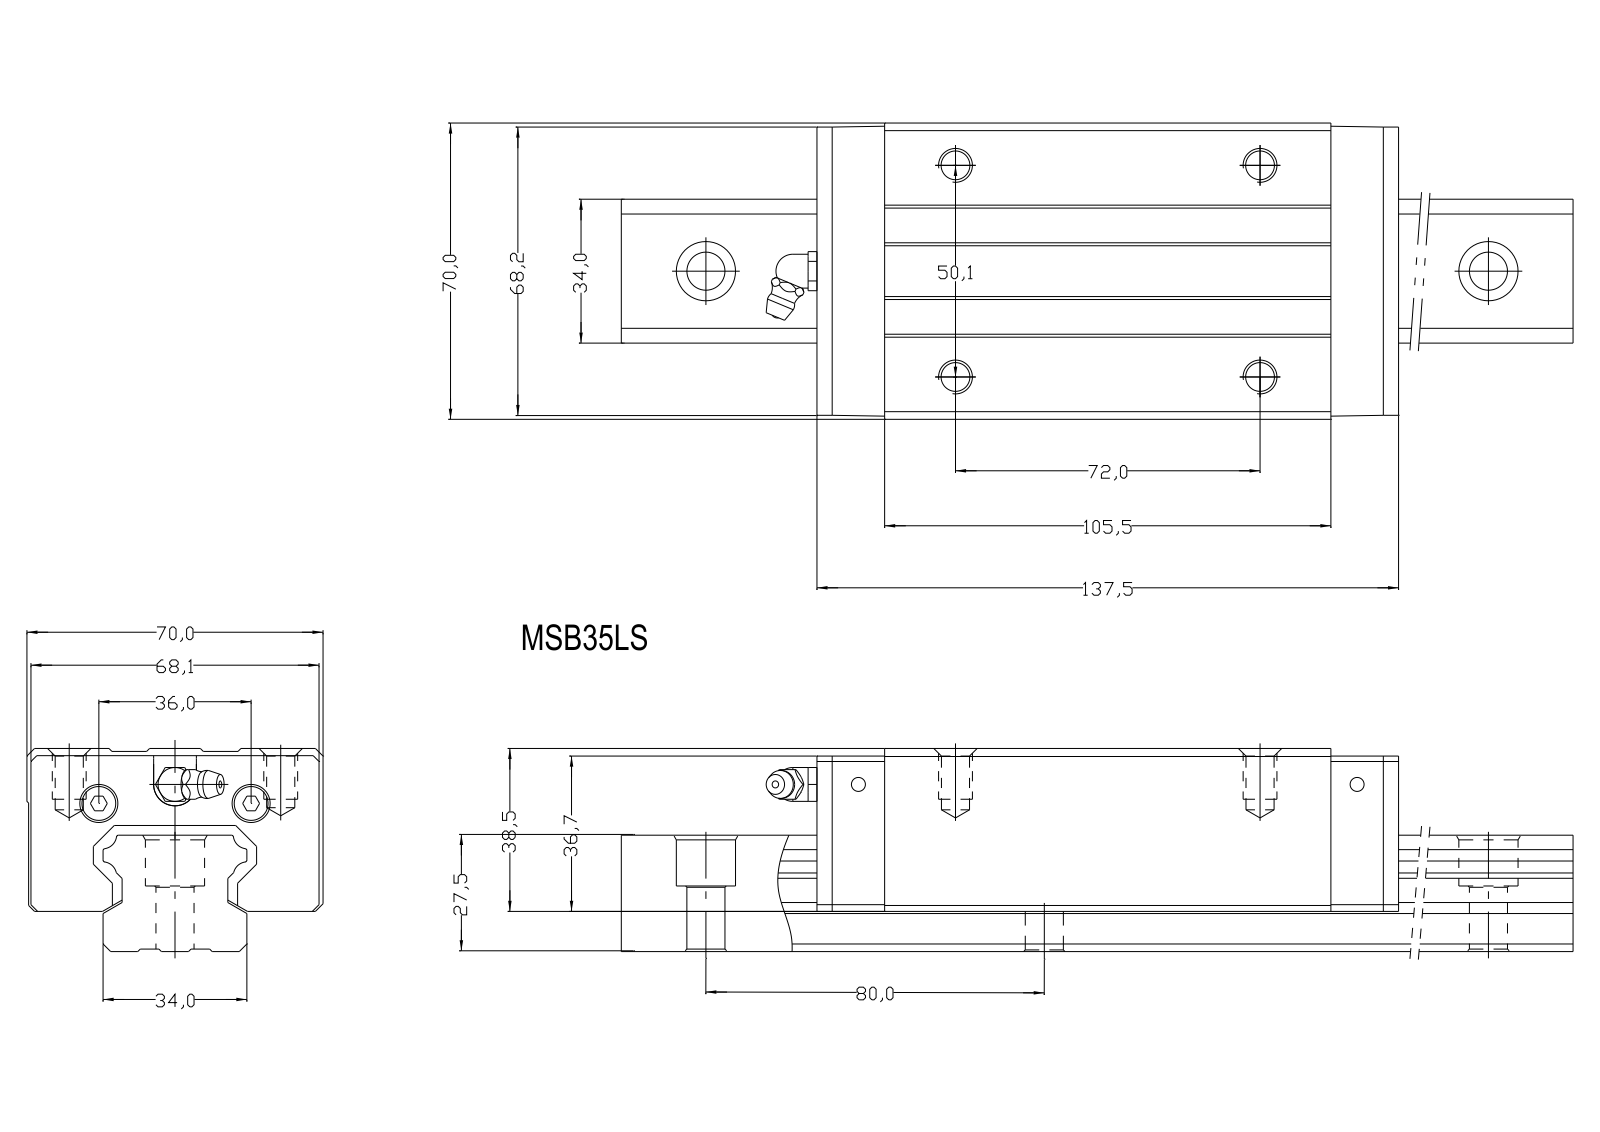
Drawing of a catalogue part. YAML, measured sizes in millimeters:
step_written_by: "Kubotek KeyCreator V6.5.2 (0407) (CONFIG_CONTROL_DESIGN)"
units: millimeters
bodies: {solids: 3, faces: 224, planar: 133, cylindrical: 74, other: 17}
overall_size: [280, 70, 48]
volume: 505805
surface_area: 82809
round_holes:
  - {diameter: 9, count: 6}
  - {diameter: 3.3, count: 4}
  - {diameter: 8, count: 4}
  - {diameter: 14, count: 4}
round_bosses_or_shafts:
  - {diameter: 8, count: 1}
partial_cylinders:
  - {radius: 0.5, count: 6}
  - {radius: 3.5, count: 4}
  - {radius: 5.1, count: 1}
face_to_face_distances: [18, 27.5, 20.5, 48, 9.5, 38.5, 29.5, 4.5, 22.5, 47.5]
hole_center_spacings: [25.32, 80.01, 87.64, 157.99, 80, 50, 72, 87.66]
